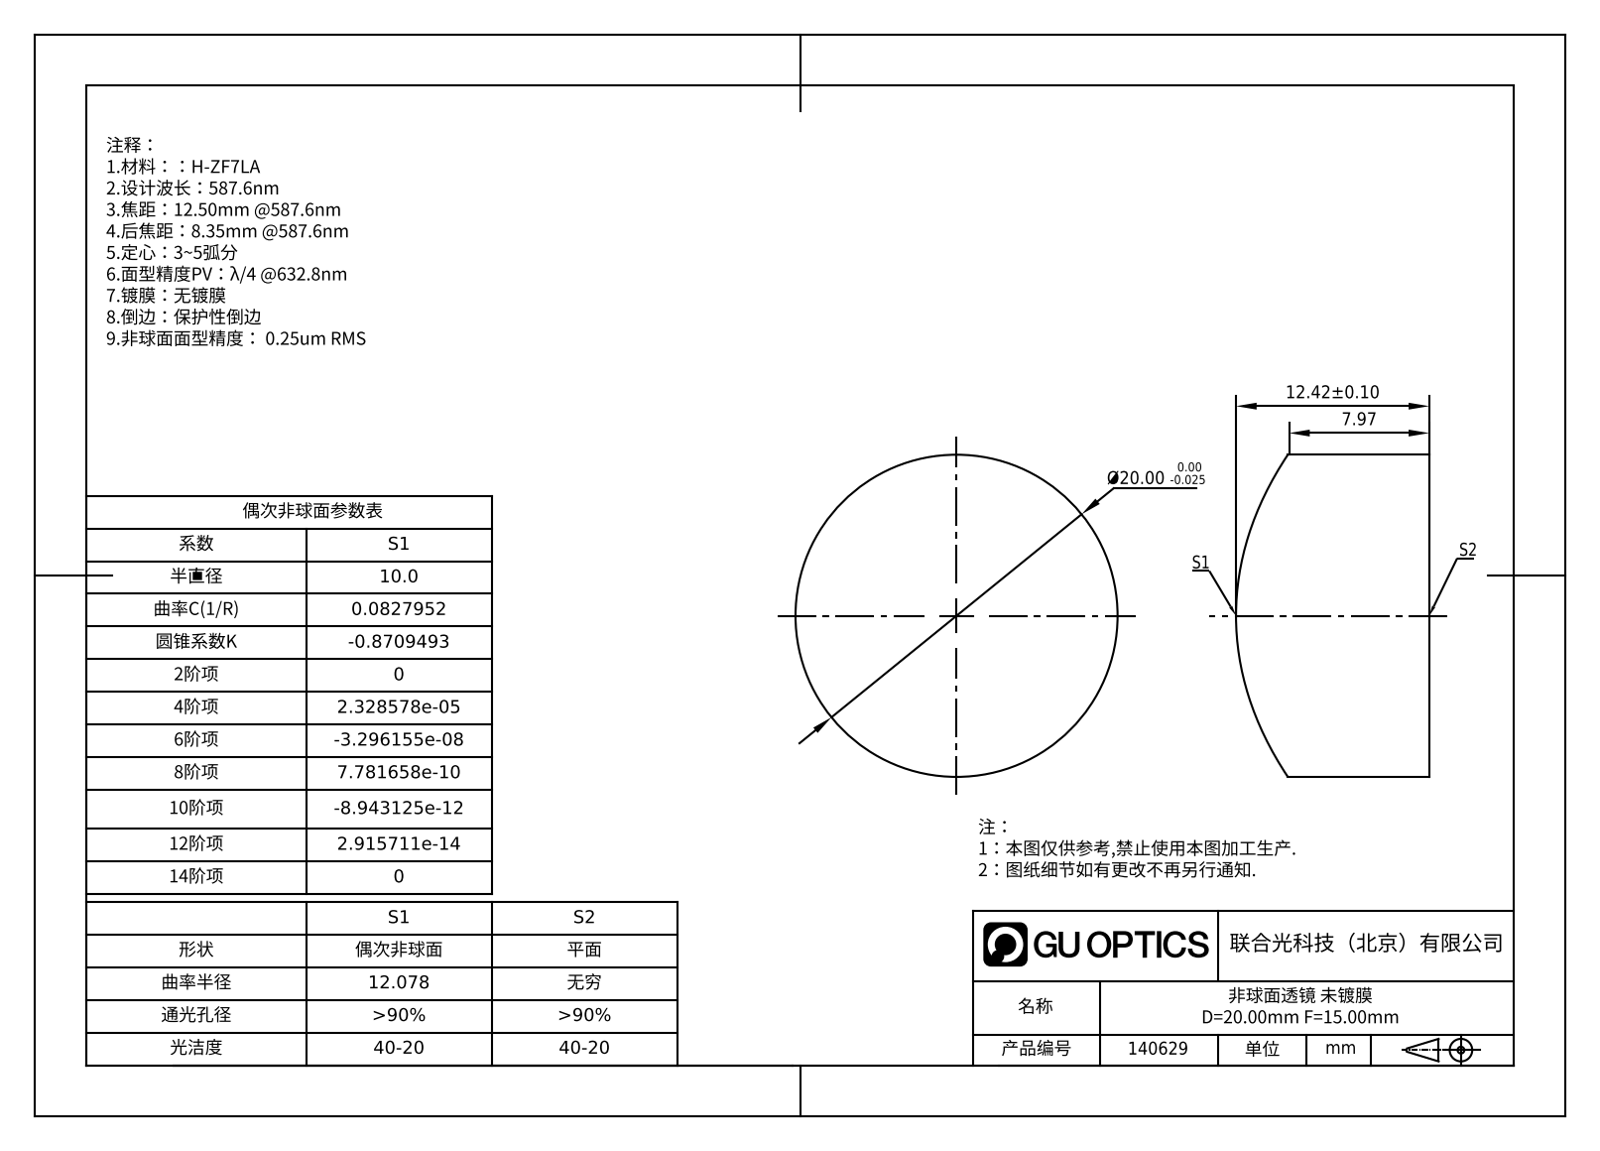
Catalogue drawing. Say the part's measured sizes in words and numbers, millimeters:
The part is named "GLA11-020-015-H; GLA11-020-015-H.stp; surfaces 1,2.stp". Its 3-D file was written by "SolidWorks 2023 (CONFIG_CONTROL_DESIGN)". It is 1 solid with 5 faces: 1 planar, 2 cylindrical and 2 other. Overall it measures 20 by 20 by 12.42 millimeters. Its volume is 3 218 cubic millimeters and its surface area 1 187 square millimeters. Round bosses or shafts: 1 of diameter 20.
